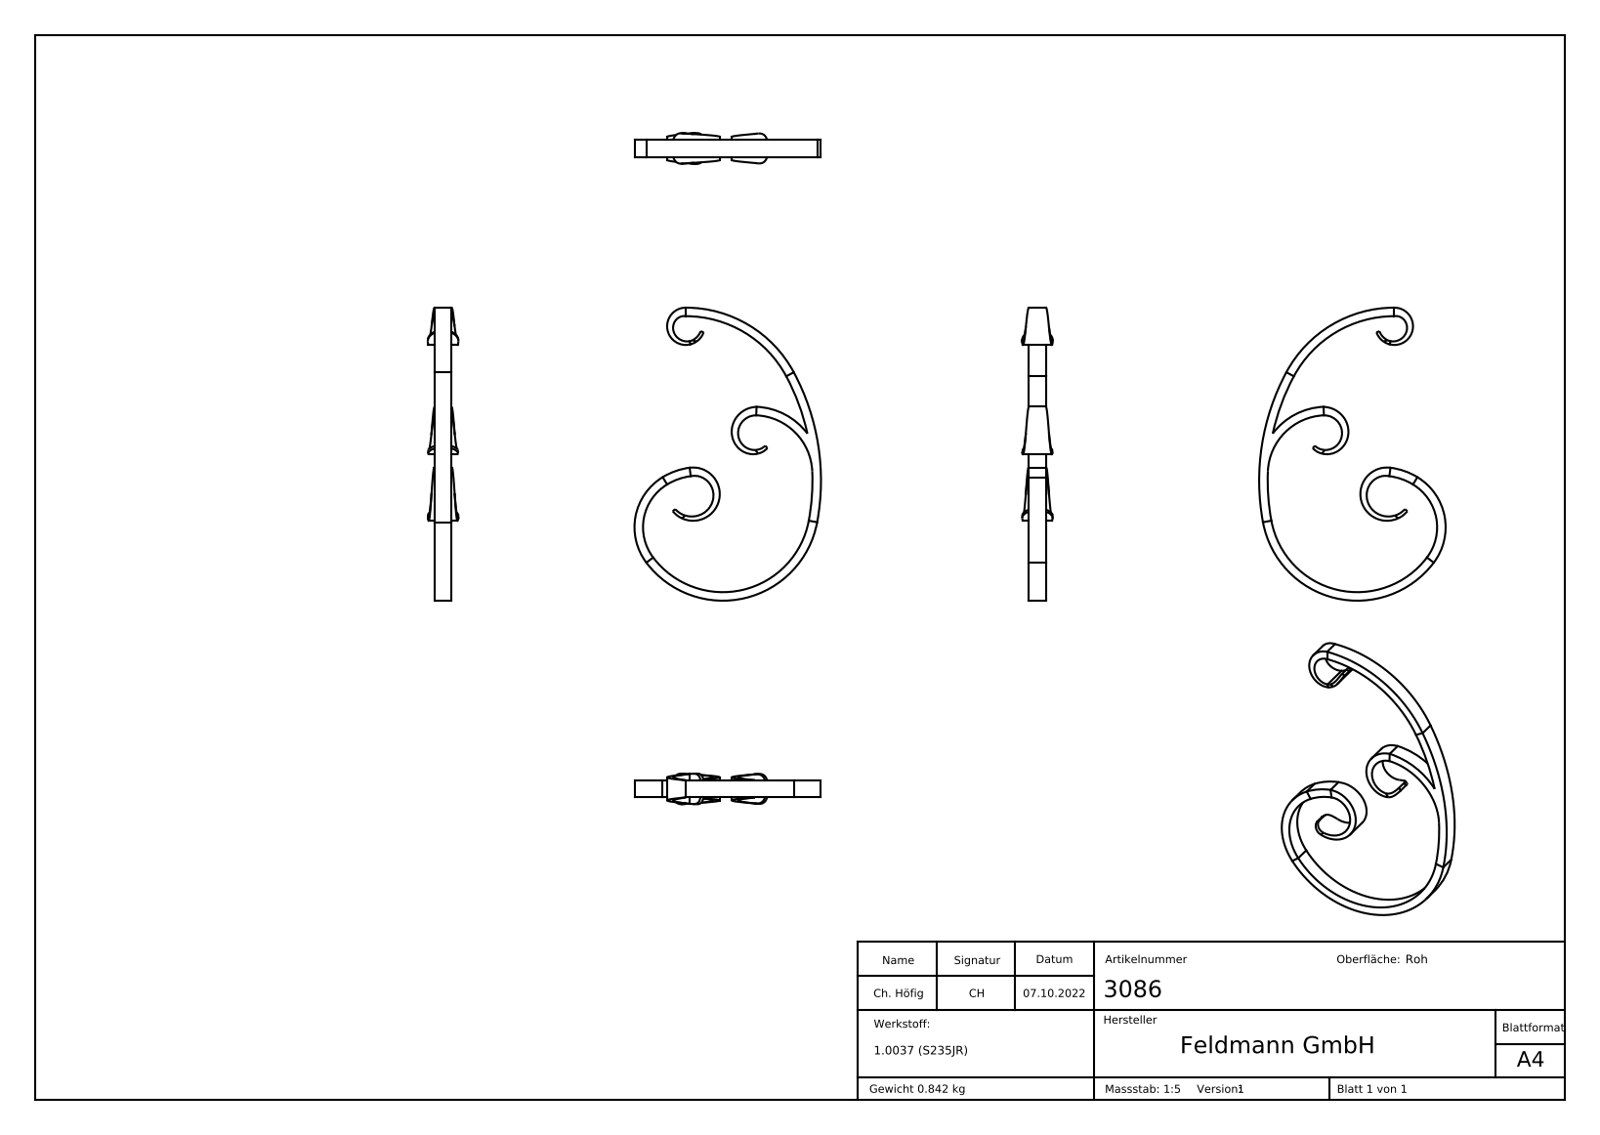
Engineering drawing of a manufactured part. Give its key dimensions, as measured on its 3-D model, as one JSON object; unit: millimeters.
{"part_name": "3086", "step_written_by": "SolidWorks 2018 (CONFIG_CONTROL_DESIGN)", "units": "millimeters", "bodies": {"solids": 1, "faces": 267, "planar": 95, "cylindrical": 33, "other": 139}, "overall_size": [275, 175, 28.77], "volume_mm3": 107909, "surface_area_mm2": 43178, "partial_cylinders_radius": [[55, 2], [47, 1], [57, 1], [63, 1], [65, 1], [82, 1], [90, 1], [107, 1]], "face_to_face_distances": [16, 1.14, 1.25, 2.2, 0.34, 6.99, 9.01, 1.37, 3.66, 0.32]}
